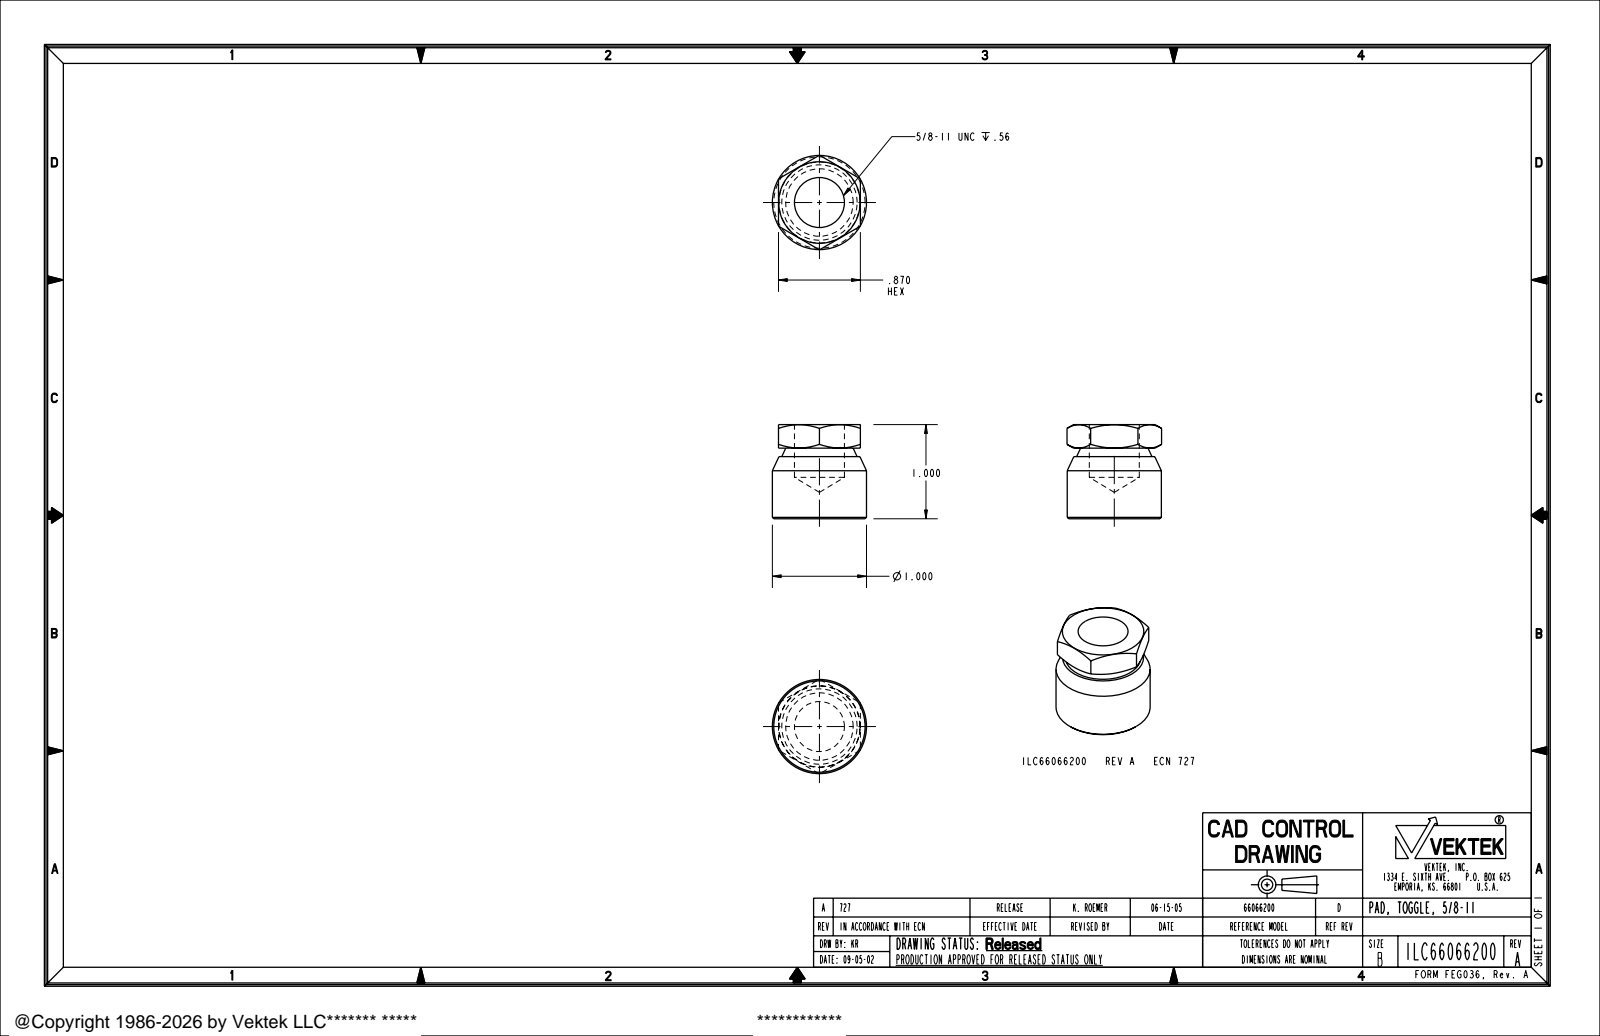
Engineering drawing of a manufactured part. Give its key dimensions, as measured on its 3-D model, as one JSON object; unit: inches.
{"part_name": "ILC66066200", "step_written_by": "PRO/ENGINEER BY PARAMETRIC TECHNOLOGY CORPORATION, 2004290 (AUTOMOTIVE_DESIGN_CC2)", "units": "inches", "bodies": {"solids": 1, "faces": 26, "planar": 10, "cylindrical": 4, "other": 12}, "overall_size": [1.005, 1, 1], "volume_in3": 0.569, "surface_area_in2": 5.724, "round_holes": [[0.531, 1]], "round_bosses_or_shafts": [[1, 1]], "face_to_face_distances": [1, 0.87, 0.75, 0.25, 0.66, 0.09, 0.34]}
